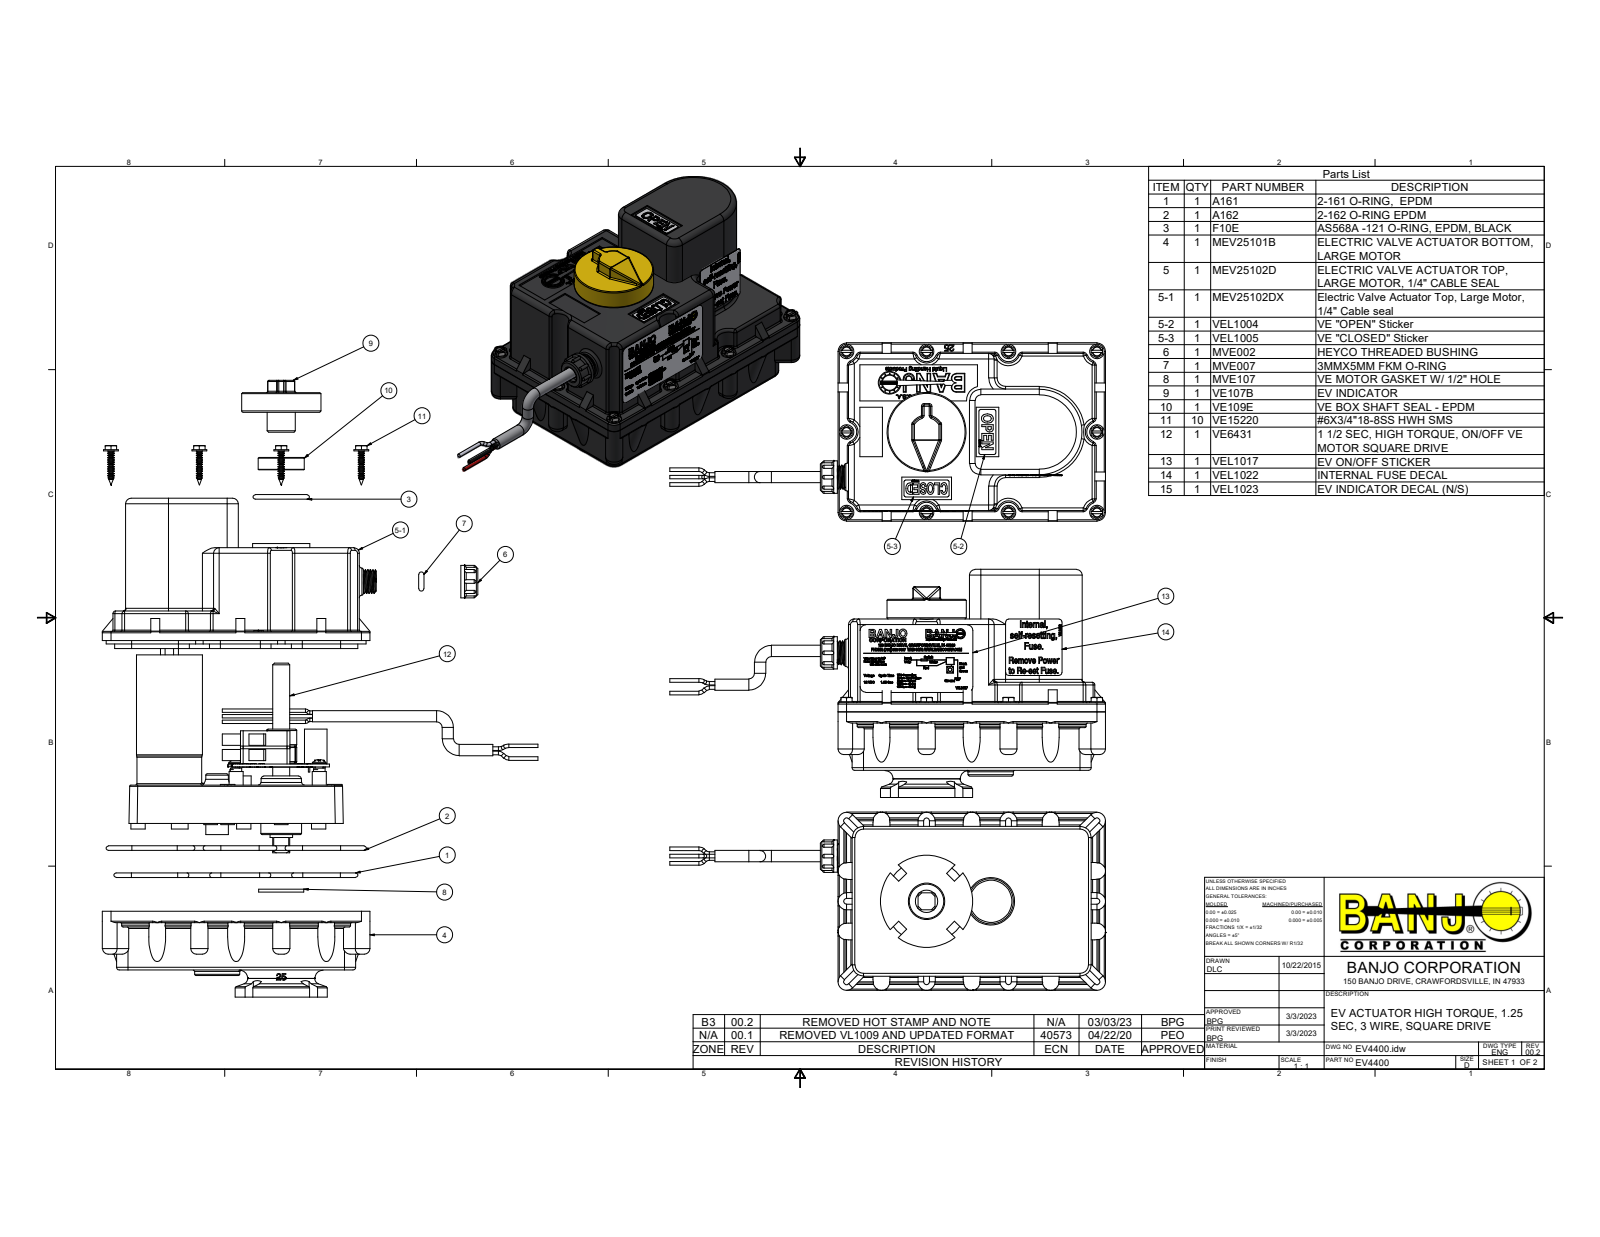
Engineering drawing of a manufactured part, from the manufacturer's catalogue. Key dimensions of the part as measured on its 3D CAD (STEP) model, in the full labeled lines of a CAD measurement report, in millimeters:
Part name (STEP PRODUCT): EV4400; MEV25101B; MEV25102D; MEV25102DX (+8 more)
STEP written by: Autodesk Inventor 2022 (AUTOMOTIVE_DESIGN)
Units: millimetres
Bodies: 42 solids, 10235 faces (5383 planar, 1099 cylindrical, 3753 other)
Overall size (bounding box): 245.3 × 128.4 × 100.3
Volume: 674 200 mm³ · Surface area: 260 600 mm²
Round holes (diameter × count): ⌀2.8 ×10, ⌀4.1 ×10, ⌀5.1 ×10, ⌀1.3 ×8, ⌀2 ×8, ⌀1.2 ×6, ⌀3 ×6, ⌀3.8 ×6, ⌀0.4 ×4, ⌀3.3 ×4, ⌀4.5 ×4, ⌀1 ×3
Round bosses / shafts (diameter × count): ⌀6.4 ×13, ⌀8.3 ×10, ⌀3.5 ×10, ⌀2 ×9, ⌀2.6 ×8, ⌀8 ×6, ⌀7.6 ×6, ⌀1.9 ×5
Partial cylindrical surfaces — rounded edges, fillets, slot ends (radius × count): R0.8 ×93, R0.9 ×43, R1.5 ×41, R3.2 ×28, R0.5 ×26, R8 ×24, R12.7 ×24, R9.9 ×16
Main face-to-face distances: 3.2, 85.2, 20.1, 26, 82, 7, 65.2, 31.1, 1.1, 7
Hole centre spacings: 42.7, 52.3, 60.4, 45.3, 2.8, 8.8, 12.5, 30.2
